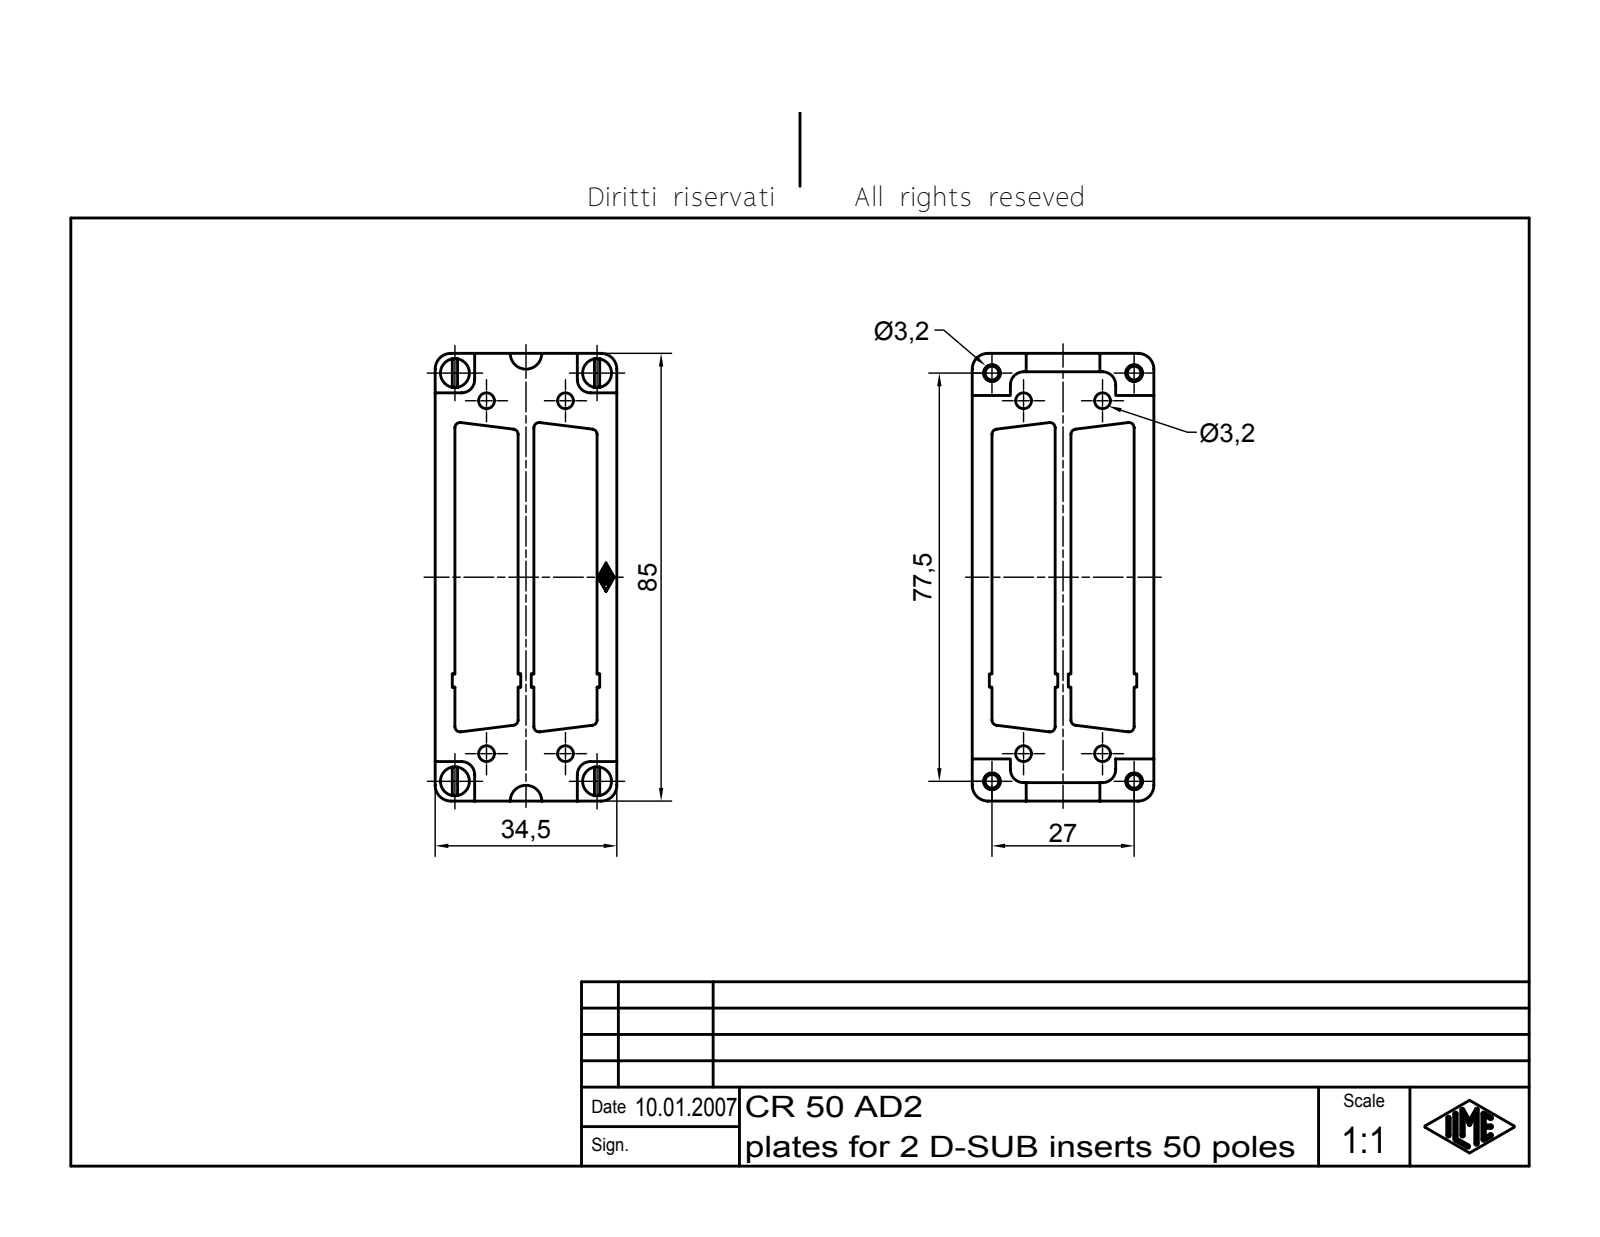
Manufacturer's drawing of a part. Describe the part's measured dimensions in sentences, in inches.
The part is named "CR 50 AD2". Its 3-D file was written by "Autodesk Inventor 7 (AUTOMOTIVE_DESIGN)". It is 1 solid with 215 faces: 129 planar, 70 cylindrical and 16 other. Overall it measures 3.346 by 1.358 by 0.551 inches. Its volume is 0.41 cubic inches and its surface area 10.54 square inches. Round holes: 4 of diameter 0.118, 4 of diameter 0.126. Round bosses or shafts: 4 of diameter 0.217, 4 of diameter 0.118. Partial cylindrical surfaces (rounded edges, fillets, slot ends): 14 of radius 0.004, 8 of radius 0.039, 8 of radius 0.098, 6 of radius 0.118. The main face-to-face distances are 0.118, 0.315, 0.148, 0.472, 0.591, 0.62, 0.738, 1.211, 0.276, 1.358. The hole center spacings are 0.314, 0.852, 2.854, 2.962, 0.591, 1.063, 2.638, 2.703.
